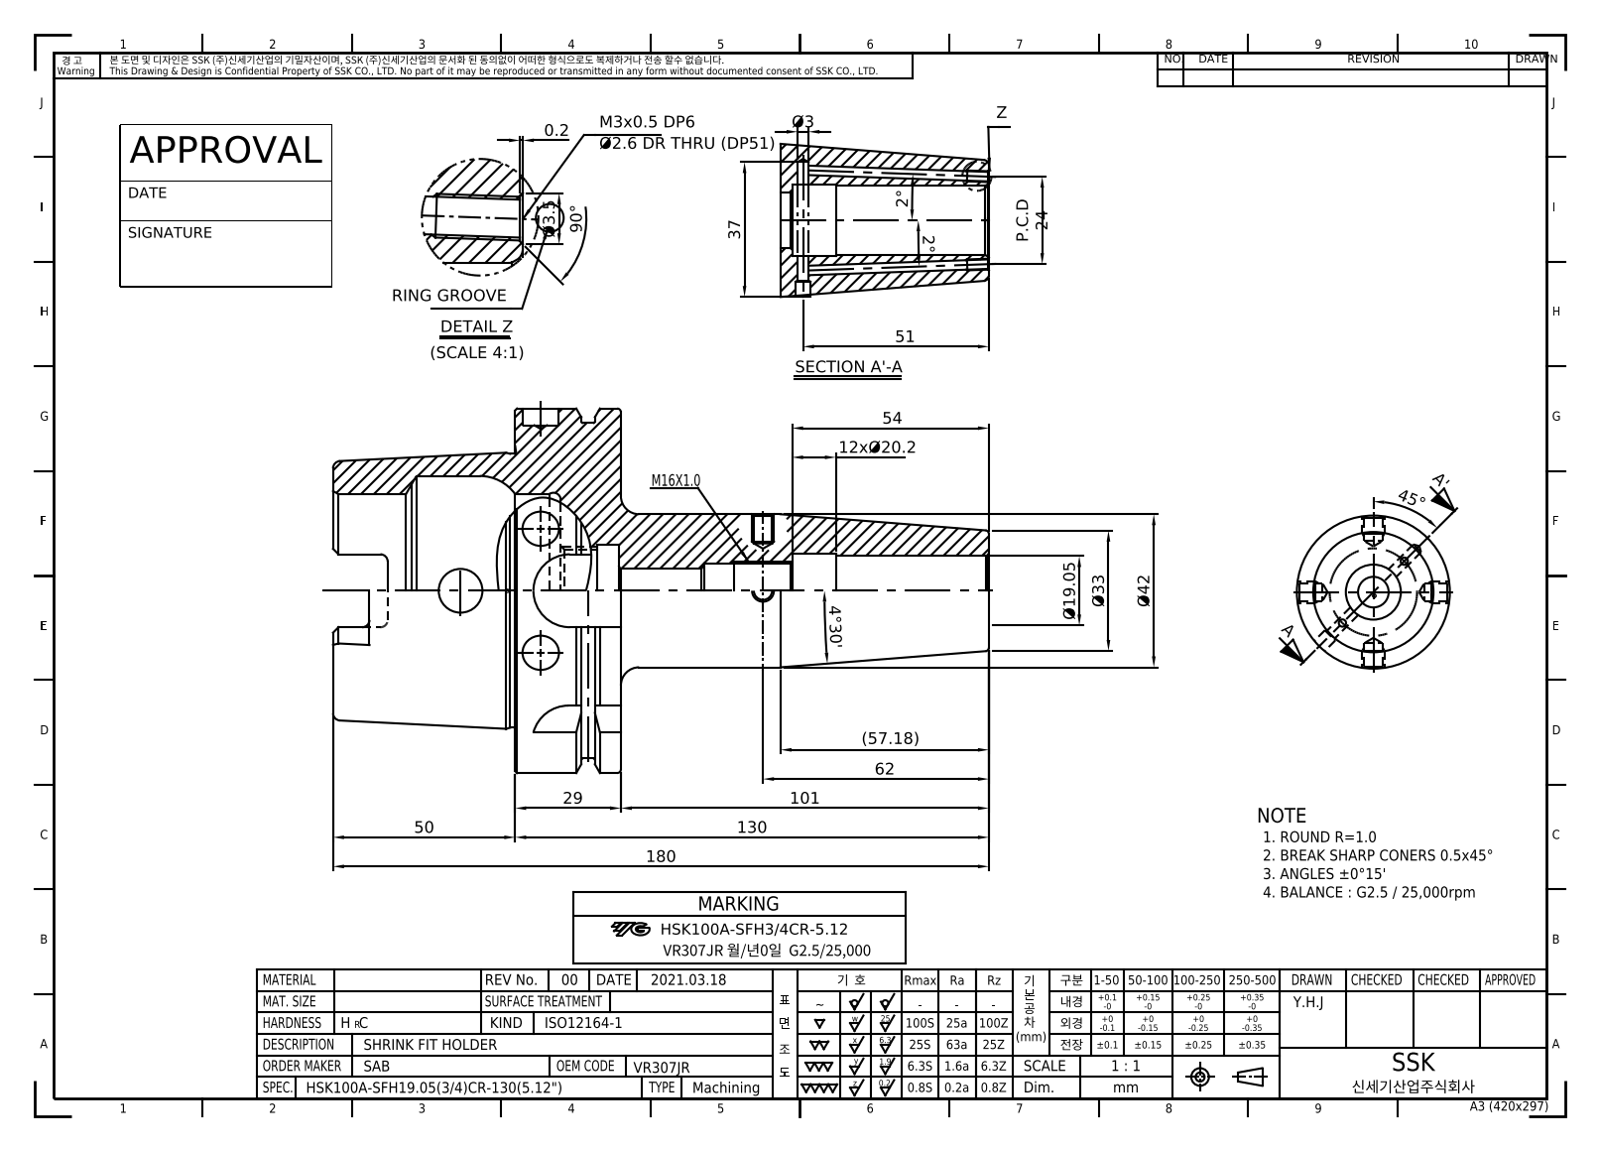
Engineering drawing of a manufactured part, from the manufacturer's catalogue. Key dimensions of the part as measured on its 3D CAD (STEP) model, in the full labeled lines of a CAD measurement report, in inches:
Part name (STEP PRODUCT): LO-HSK100A-SFH19.05CR-130
STEP written by: Autodesk Inventor 2022 (AUTOMOTIVE_DESIGN)
Units: inches
Bodies: 1 solid, 119 faces (38 planar, 37 cylindrical, 44 other)
Overall size (bounding box): 7.087 × 3.937 × 3.937
Volume: 21.72 in³ · Surface area: 104.3 in²
Round holes (diameter × count): ⌀0.097 ×2, ⌀0.472 ×2, ⌀0.394 ×1, ⌀0.587 ×1, ⌀0.75 ×1, ⌀0.797 ×1, ⌀0.881 ×1, ⌀0.984 ×1, ⌀2.087 ×1, ⌀2.48 ×1
Round bosses / shafts (diameter × count): ⌀3.937 ×1, ⌀3.622 ×1, ⌀2.969 ×1, ⌀1.654 ×1
Partial cylindrical surfaces — rounded edges, fillets, slot ends (radius × count): R0.079 ×6, R0.192 ×4, R0.394 ×4
Main face-to-face distances: 1.142, 0.492, 0.65, 2.461, 1.969, 3.11, 3.465, 7.087, 5.118, 4.626
